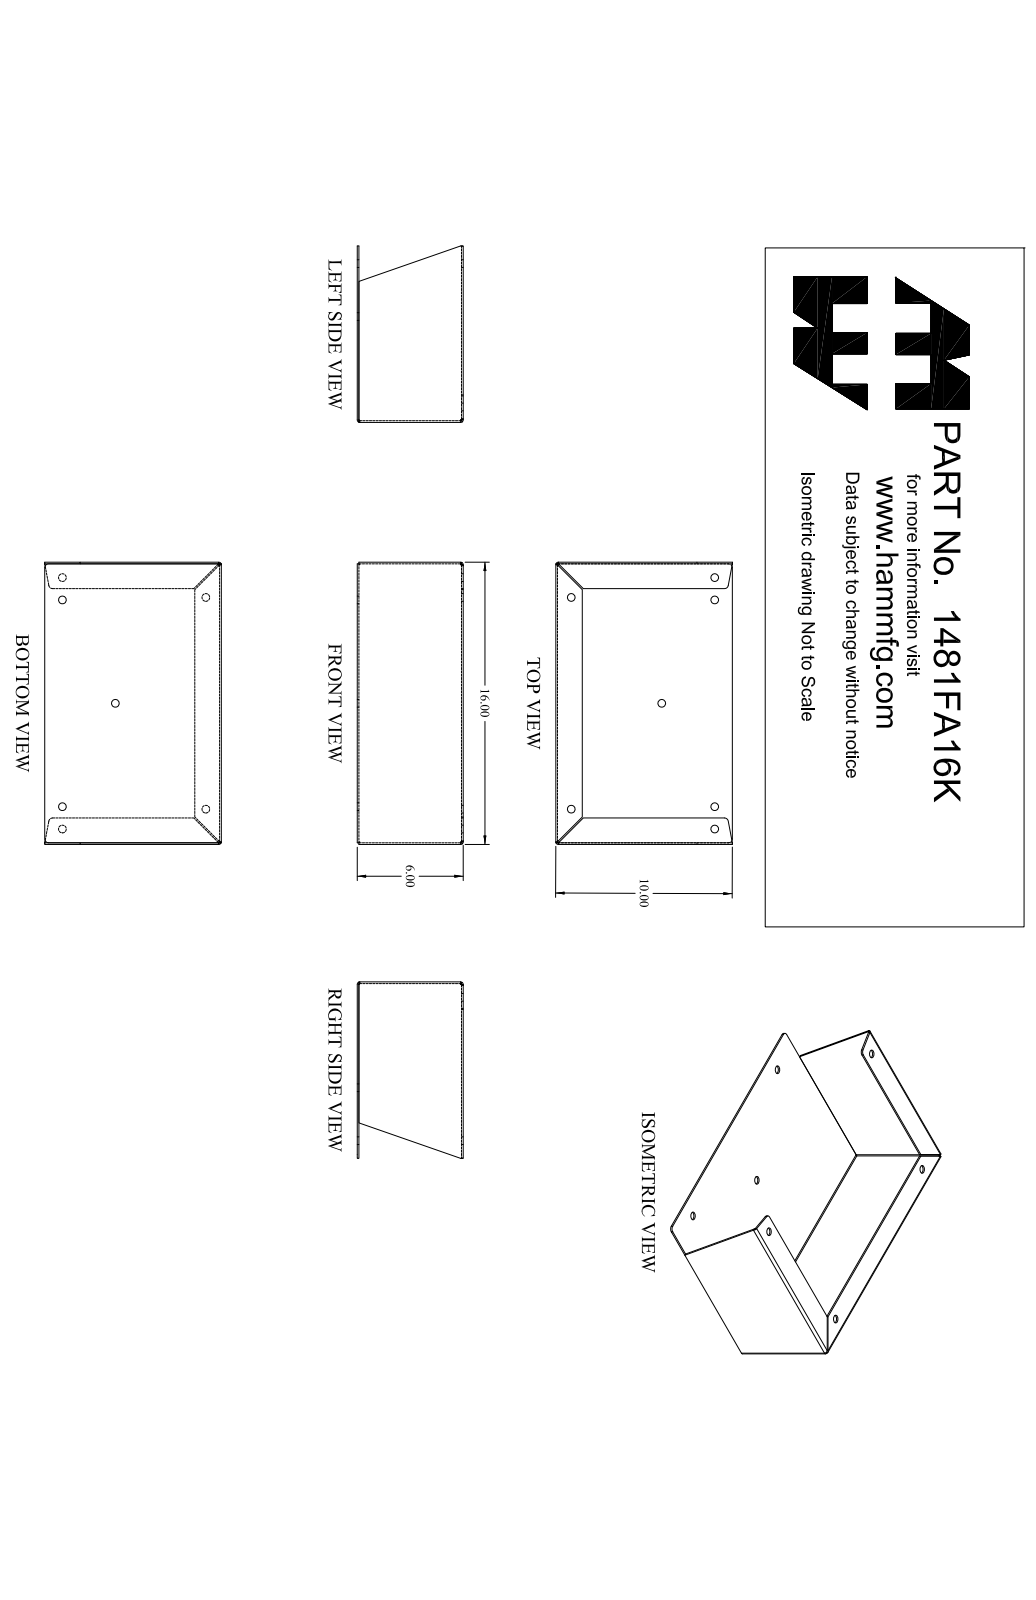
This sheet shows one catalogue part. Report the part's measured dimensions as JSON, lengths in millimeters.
{"part_name": "1481FA16K_Default", "step_written_by": "SolidWorks 2019 (CONFIG_CONTROL_DESIGN)", "units": "millimeters", "bodies": {"solids": 1, "faces": 78, "planar": 42, "cylindrical": 30, "other": 6}, "overall_size": [406.4, 254, 152.4], "volume_mm3": 622200, "surface_area_mm2": 522700, "round_holes": [[11.1, 7]], "partial_cylinders_radius": [[1.2, 6], [3.6, 6], [5.6, 4]], "face_to_face_distances": [2.4, 2.4, 404, 406.4, 401.6, 147.6, 150, 150, 152.4, 38.1], "hole_center_spacings": [167.2, 200.4, 206.4, 208.3, 365.1, 32.2, 32.2, 196.4]}
